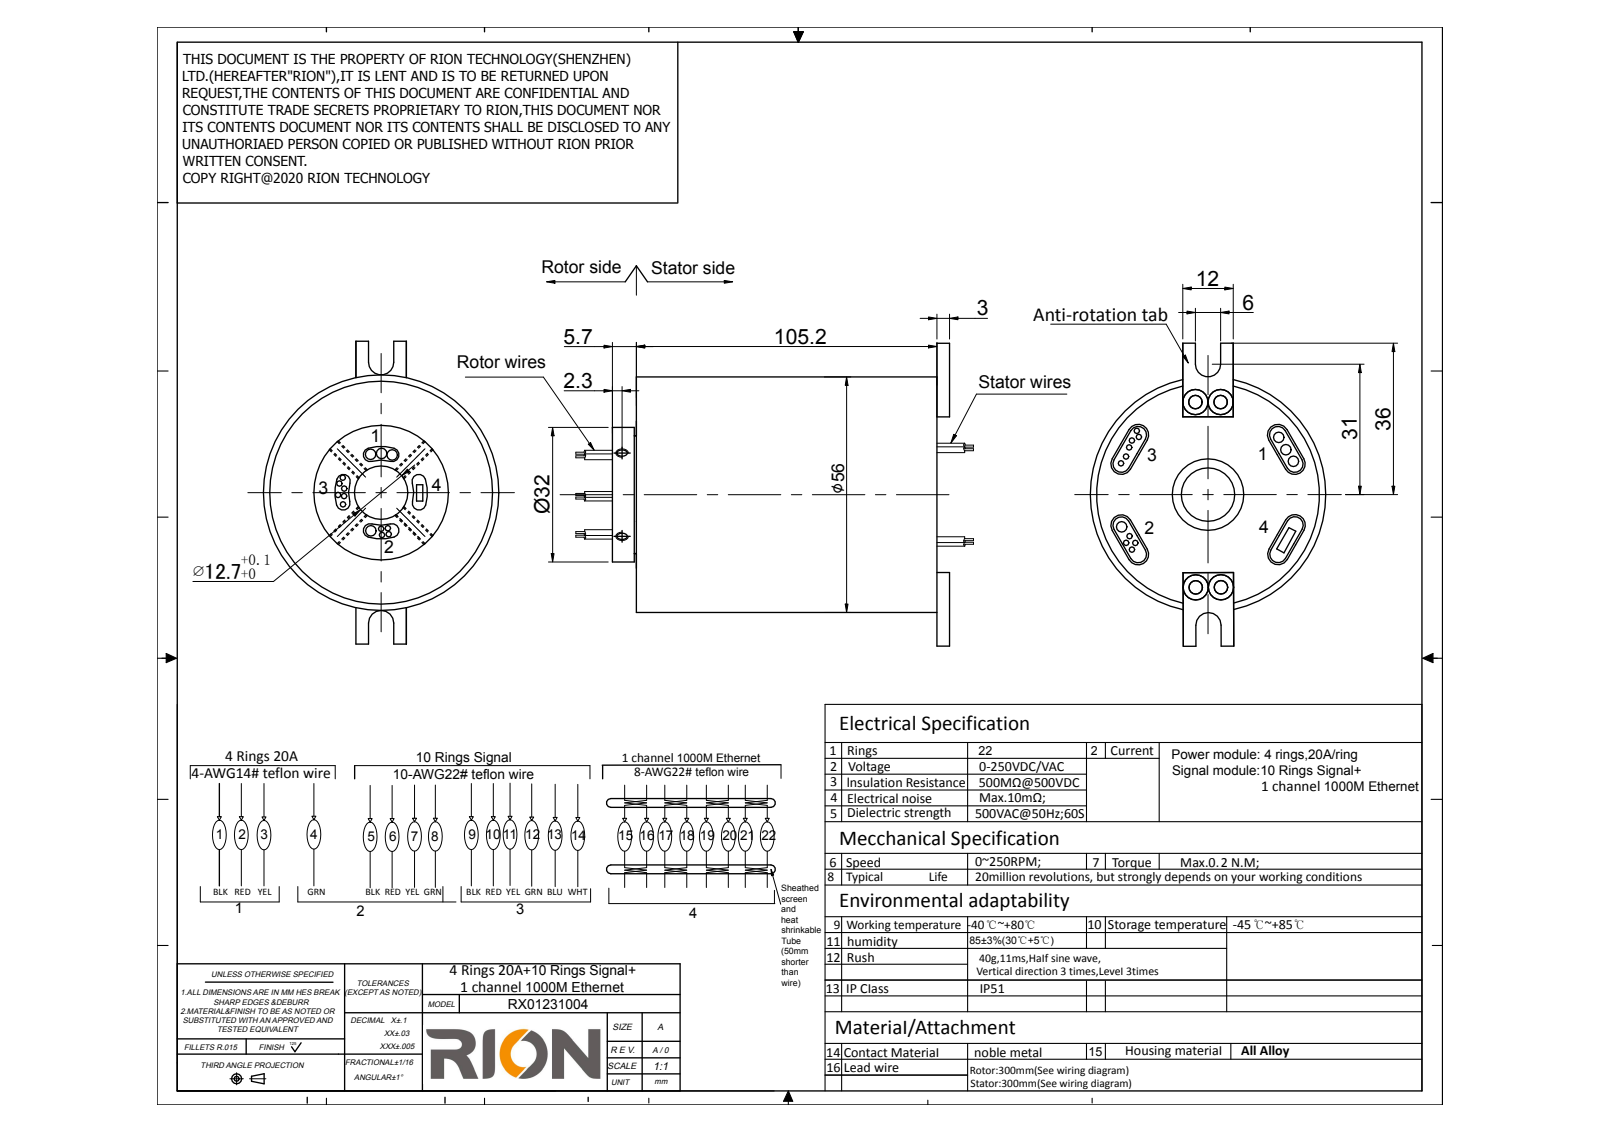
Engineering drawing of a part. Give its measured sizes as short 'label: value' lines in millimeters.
name: RX01231004
written by: SolidWorks 2014 (CONFIG_CONTROL_DESIGN)
unit: mm
bodies: 1 solid, 242 faces (86 planar, 140 cylindrical, 16 other)
size: 129.4 × 72 × 56
volume: 250 580 mm³; area: 33 368 mm²
holes: 6× ⌀2.5, 4× ⌀3.2, 1× ⌀12.7, 1× ⌀15.8, 1× ⌀53
bosses: 20× ⌀1.3, 8× ⌀2.5, 2× ⌀4, 1× ⌀56, 1× ⌀52.9, 1× ⌀32, 1× ⌀28, 1× ⌀15.5
rounds: 8× R2, 8× R2, 4× R8.02, 4× R12.03, 2× R3
face distances: 105.2, 5.7, 110.9, 3, 113.9, 108.2, 4.6, 1.1, 106.3, 109.3
hole spacings: 22.7, 6, 45, 45.4
